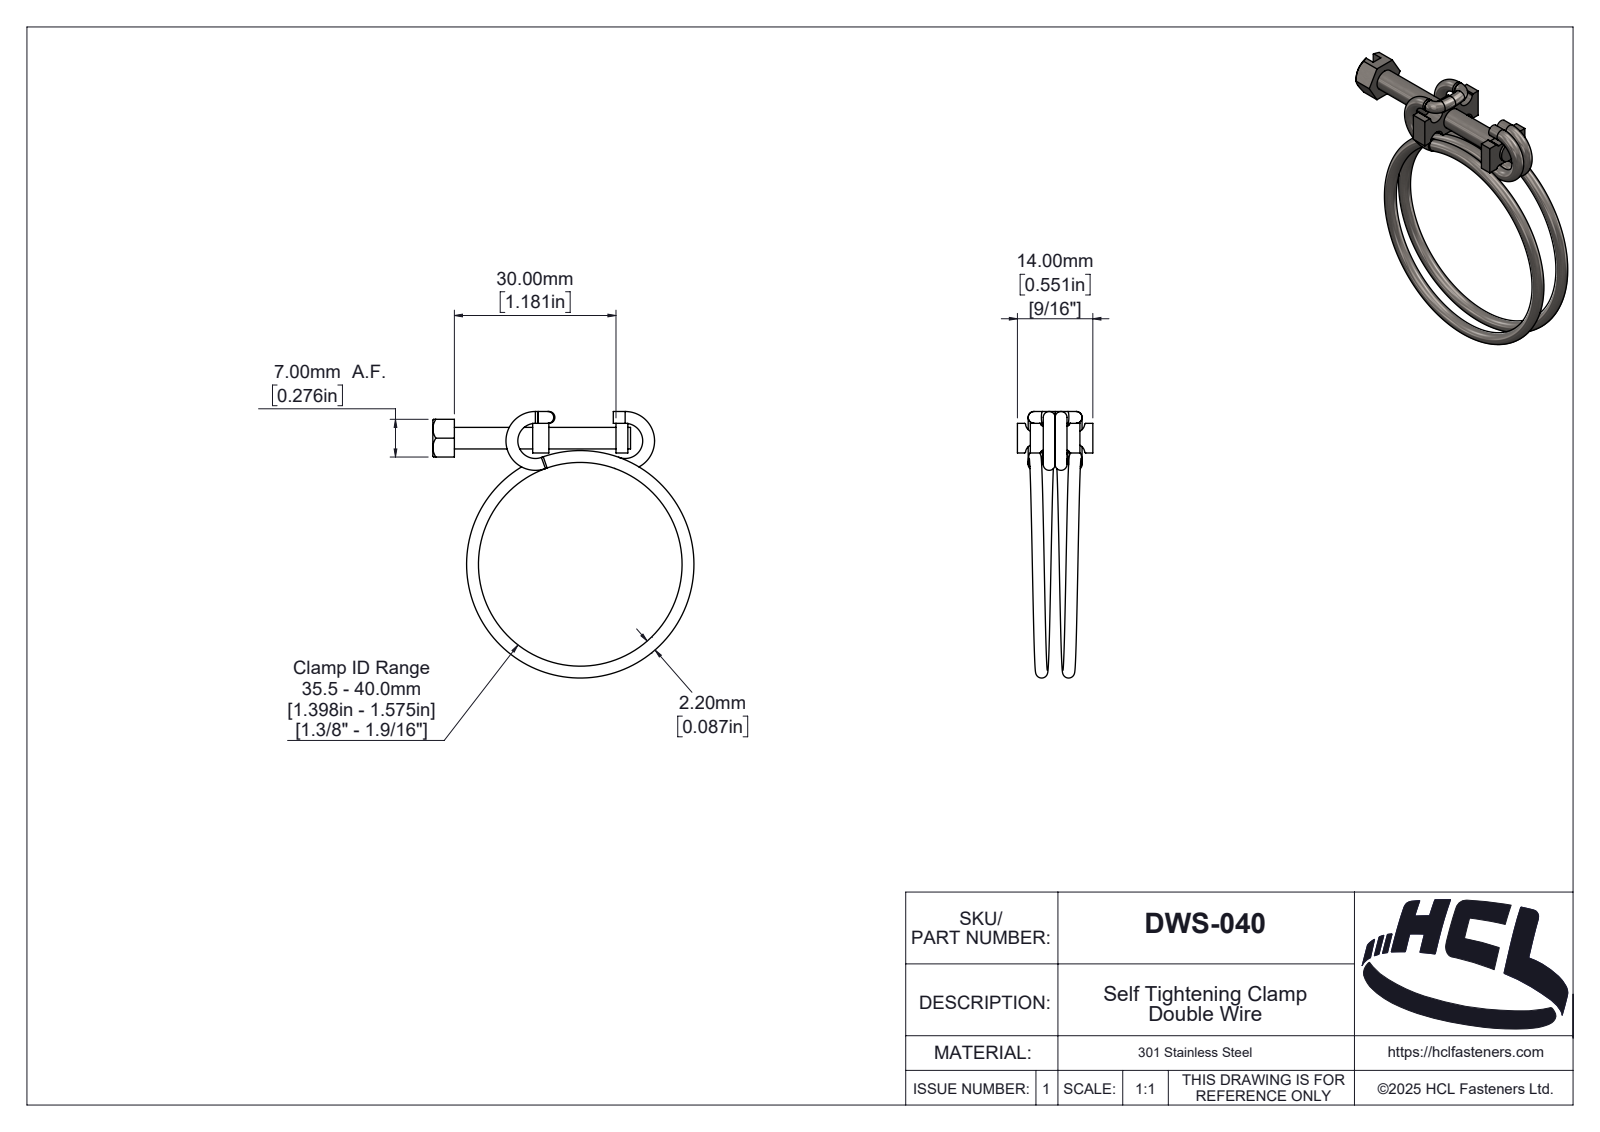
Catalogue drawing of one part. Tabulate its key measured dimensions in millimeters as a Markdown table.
| quantity | value |
| --- | --- |
| part name | DWS-040 |
| STEP written by | SolidWorks 2025 (AUTOMOTIVE_DESIGN) |
| units | millimeters |
| bodies | 6 solids, 209 faces (51 planar, 74 cylindrical, 84 other) |
| overall size | 49.45 × 48.47 × 14 |
| volume | 2 120 mm³ |
| surface area | 3 521 mm² |
| round holes (diameter × count) | 4 × 1 |
| round bosses / shafts (diameter × count) | 2.2 × 4 |
| partial cylindrical surfaces (radius × count) | 0.2 × 12, 0.5 × 4, 1.6 × 4, 0.4 × 1, 0.51 × 1, 0.53 × 1, 0.64 × 1, 0.91 × 1 |
| main face-to-face distances | 2, 3, 17.54, 7, 0.5, 17.66, 14.66, 15.46, 12.46, 2.2 |
